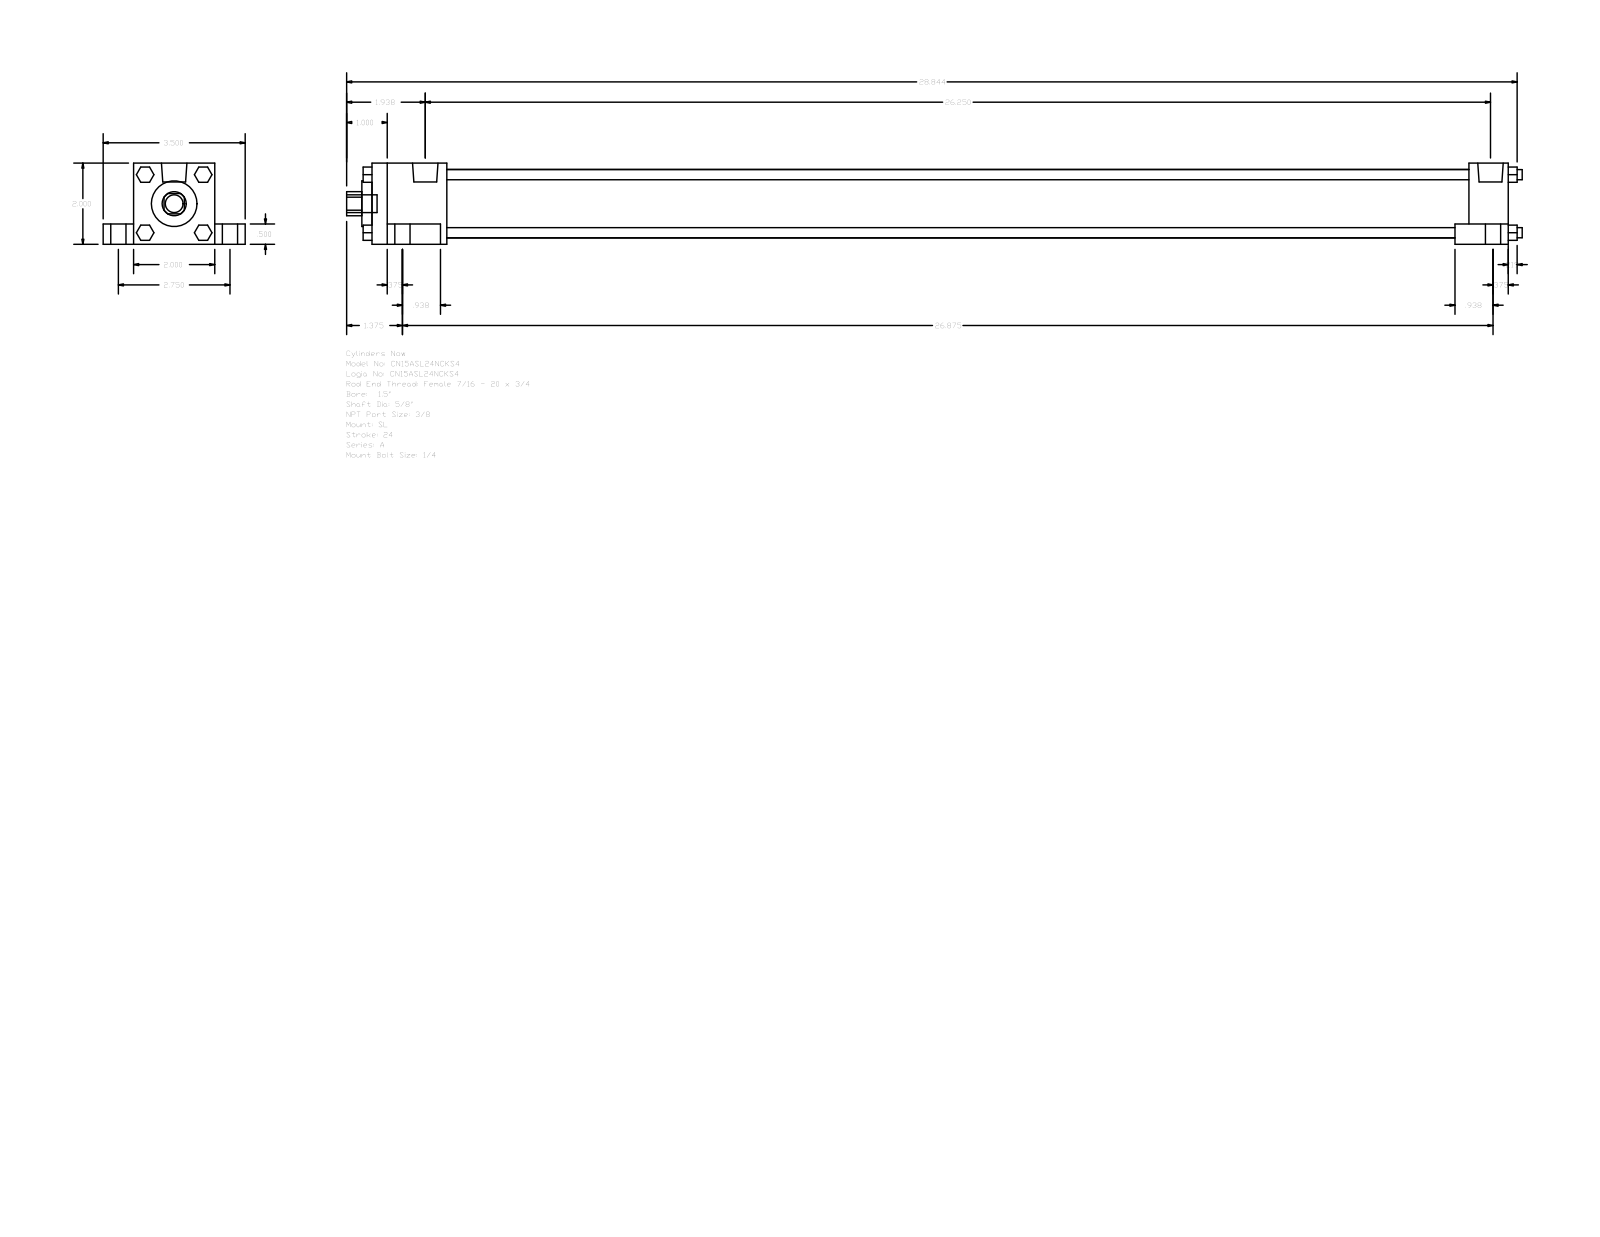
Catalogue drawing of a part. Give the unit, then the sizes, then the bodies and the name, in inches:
Units: inches
Overall size (bounding box): 28.969 × 3.5 × 2
Round holes (diameter × count): ⌀0.625 ×1, ⌀1.125 ×1, ⌀1.69 ×1
Round bosses / shafts (diameter × count): ⌀0.625 ×4, ⌀0.375 ×4, ⌀0.25 ×4, ⌀0.219 ×4, ⌀0.627 ×2, ⌀0.437 ×1
Partial cylindrical surfaces — rounded edges, fillets, slot ends (radius × count): R0.297 ×1
Main face-to-face distances: 2, 0.75, 0.5, 1.5, 2.75, 28, 0.375, 1.313, 27.031, 0.969
Bodies: 0 solids, 148 faces (112 planar, 36 cylindrical, 0 other)
Part name (STEP PRODUCT): A_SL__0150_0.625
STEP written by: GSSL Pune (CONFIG_CONTROL_DESIGN)
